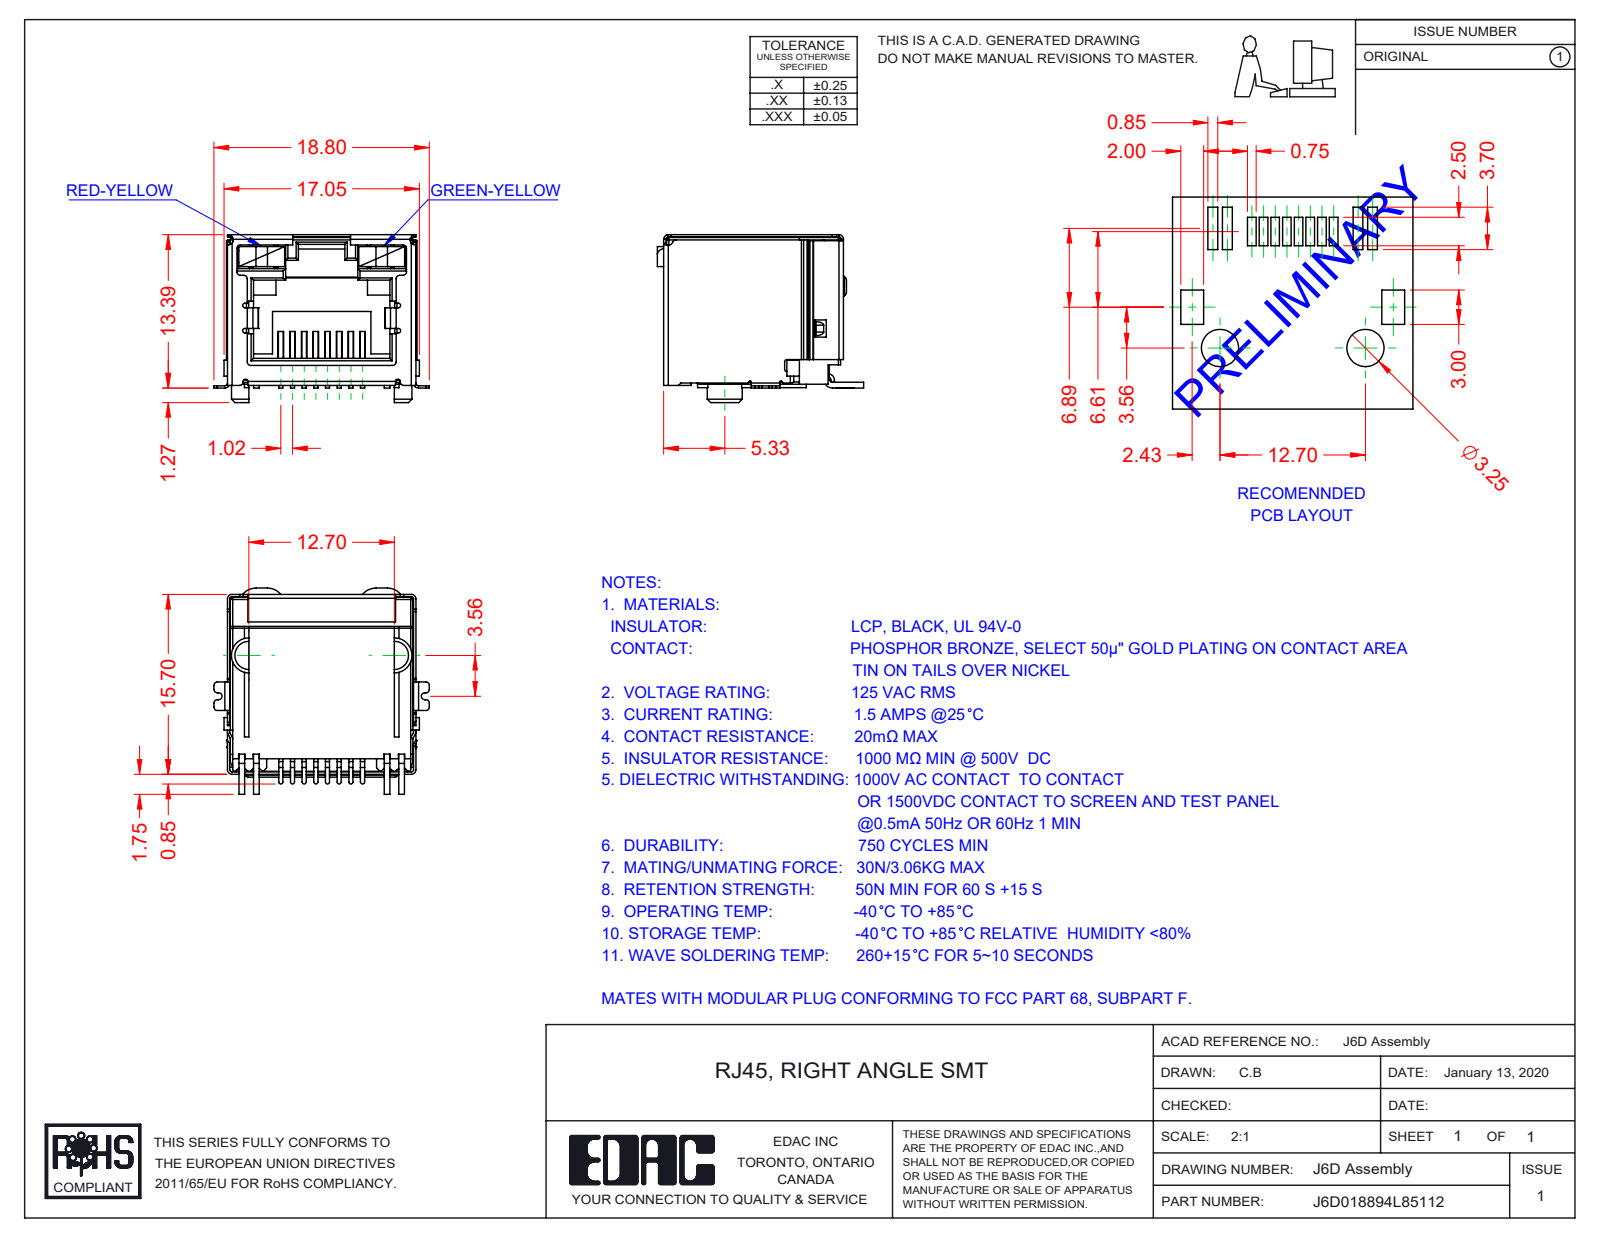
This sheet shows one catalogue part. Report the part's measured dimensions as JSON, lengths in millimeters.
{"part_name": "J6D018894L85112; 6D Contacts; 6D Shield_LED - No EMI; 6D LED LH_8-Red-Yellow (+2 more)", "step_written_by": "SolidWorks 2016 (CONFIG_CONTROL_DESIGN)", "units": "millimeters", "bodies": {"solids": 12, "faces": 899, "planar": 646, "cylindrical": 220, "other": 33}, "overall_size": [18.8, 18, 14.65], "volume_mm3": 1804, "surface_area_mm2": 4898, "partial_cylinders_radius": [[0.3, 39], [0.2, 37], [0.4, 16], [0.1, 12], [0.15, 8], [0.18, 8], [0.5, 6], [1.5, 5]], "face_to_face_distances": [16, 16.25, 16.2, 2.25, 1, 15.95, 16.05, 12.8, 0.45, 16.45]}
